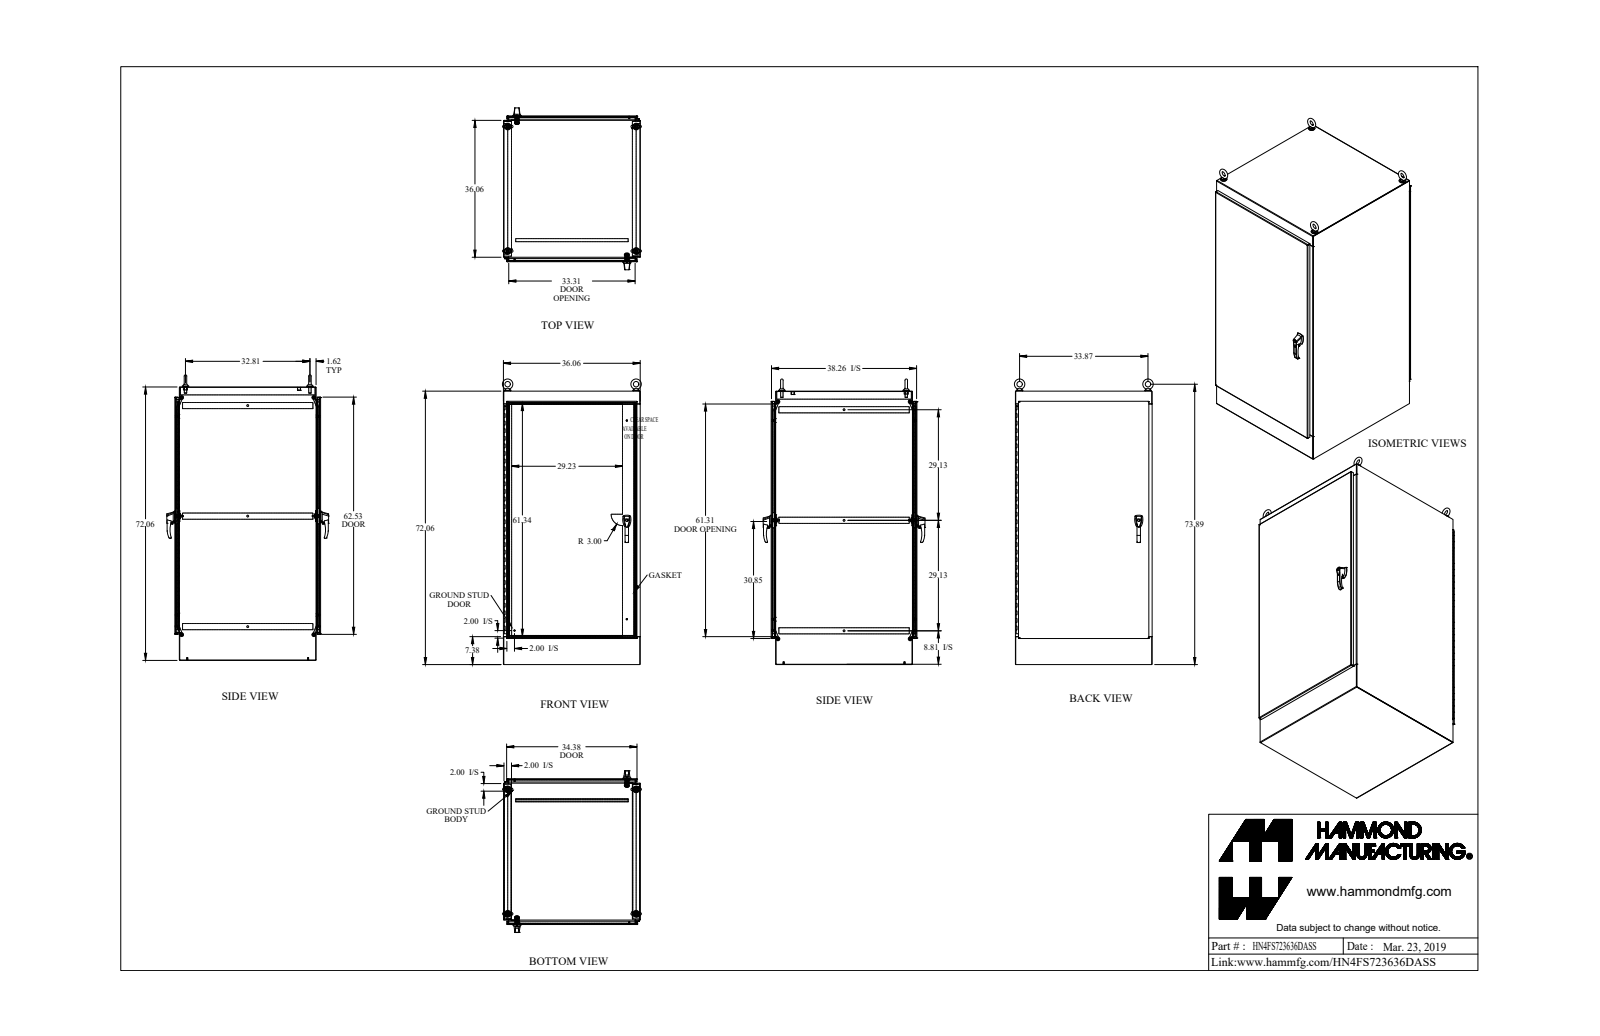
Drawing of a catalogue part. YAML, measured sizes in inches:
part_name: "HN4FS723636DASS"
step_written_by: "SolidWorks 2018 (AUTOMOTIVE_DESIGN)"
units: inches
bodies: {solids: 91, faces: 3297, planar: 1452, cylindrical: 1517, other: 328}
overall_size: [75.489, 42.664, 36.604]
volume: 1564
surface_area: 32834
round_holes:
  - {diameter: 0.304, count: 20}
  - {diameter: 0.35, count: 8}
  - {diameter: 0.25, count: 4}
  - {diameter: 0.257, count: 4}
  - {diameter: 0.28, count: 4}
  - {diameter: 0.281, count: 4}
  - {diameter: 0.313, count: 4}
  - {diameter: 0.39, count: 4}
  - {diameter: 0.413, count: 4}
  - {diameter: 0.625, count: 4}
  - {diameter: 0.68, count: 4}
  - {diameter: 0.75, count: 4}
round_bosses_or_shafts:
  - {diameter: 1.75, count: 4}
  - {diameter: 1.5, count: 4}
  - {diameter: 1.25, count: 4}
  - {diameter: 1, count: 4}
  - {diameter: 0.75, count: 4}
  - {diameter: 0.738, count: 4}
  - {diameter: 0.63, count: 4}
  - {diameter: 0.625, count: 4}
partial_cylinders:
  - {radius: 0.125, count: 44}
  - {radius: 0.043, count: 42}
  - {radius: 0.138, count: 36}
  - {radius: 0.018, count: 32}
  - {radius: 0.048, count: 26}
  - {radius: 0.143, count: 26}
  - {radius: 0.5, count: 26}
  - {radius: 0.06, count: 21}
face_to_face_distances: [0.095, 35.965, 38.339, 35.87, 36.06, 71.965, 38.244, 38.434, 1.187, 37.152]
hole_center_spacings: [6, 34.849, 12, 36.365, 18, 38.761, 24, 41.886]
